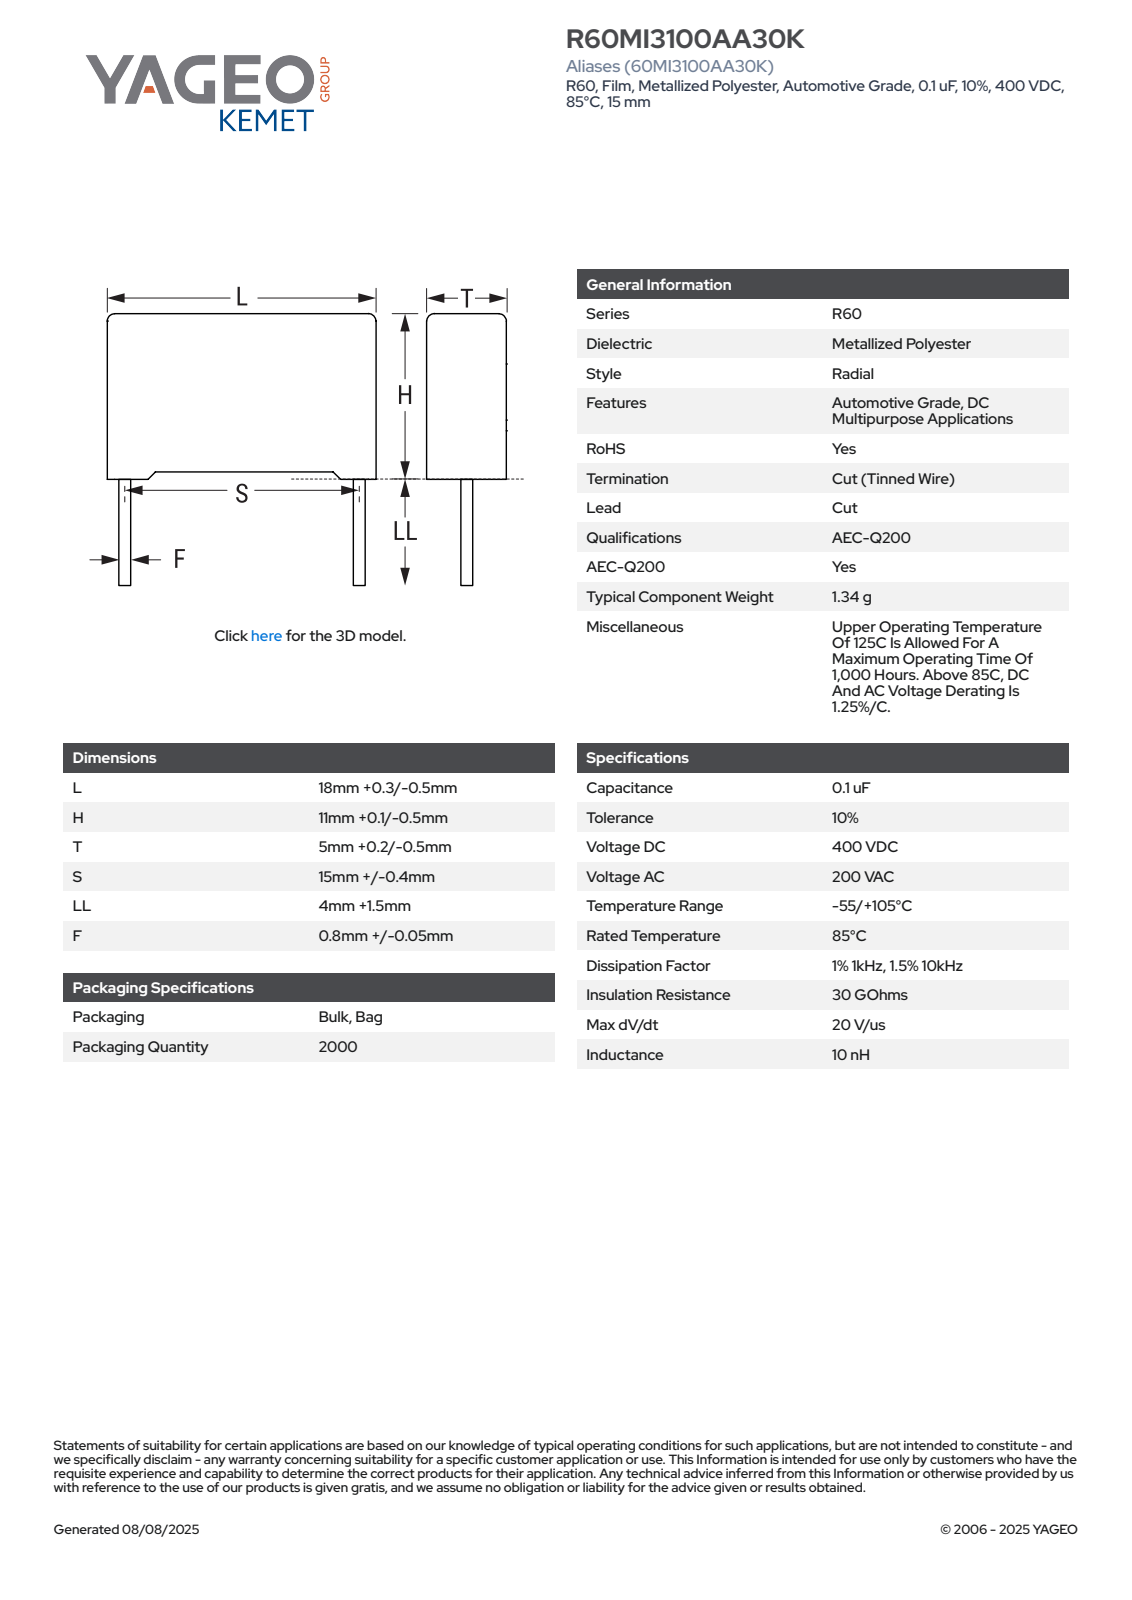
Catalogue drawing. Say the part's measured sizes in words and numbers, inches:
The part is named "CFR_RB2_18X11X5_L18.3H11.1T5.2S15LL5.5F0.85". Its 3-D file was written by "SolidWorks 2021 (AUTOMOTIVE_DESIGN)". It is 4 solids with 85 faces: 77 planar, 8 cylindrical and 0 other. Overall it measures 0.72 by 0.654 by 0.205 inches. Its volume is 0.061 cubic inches and its surface area 1.2 square inches. Round bosses or shafts: 2 of diameter 0.033. Partial cylindrical surfaces (rounded edges, fillets, slot ends): 4 of radius 0.02. The main face-to-face distances are 0.205, 0.407, 0.72, 0.024, 0.181, 0.015, 0.422, 0.015, 0.03, 0.437.
